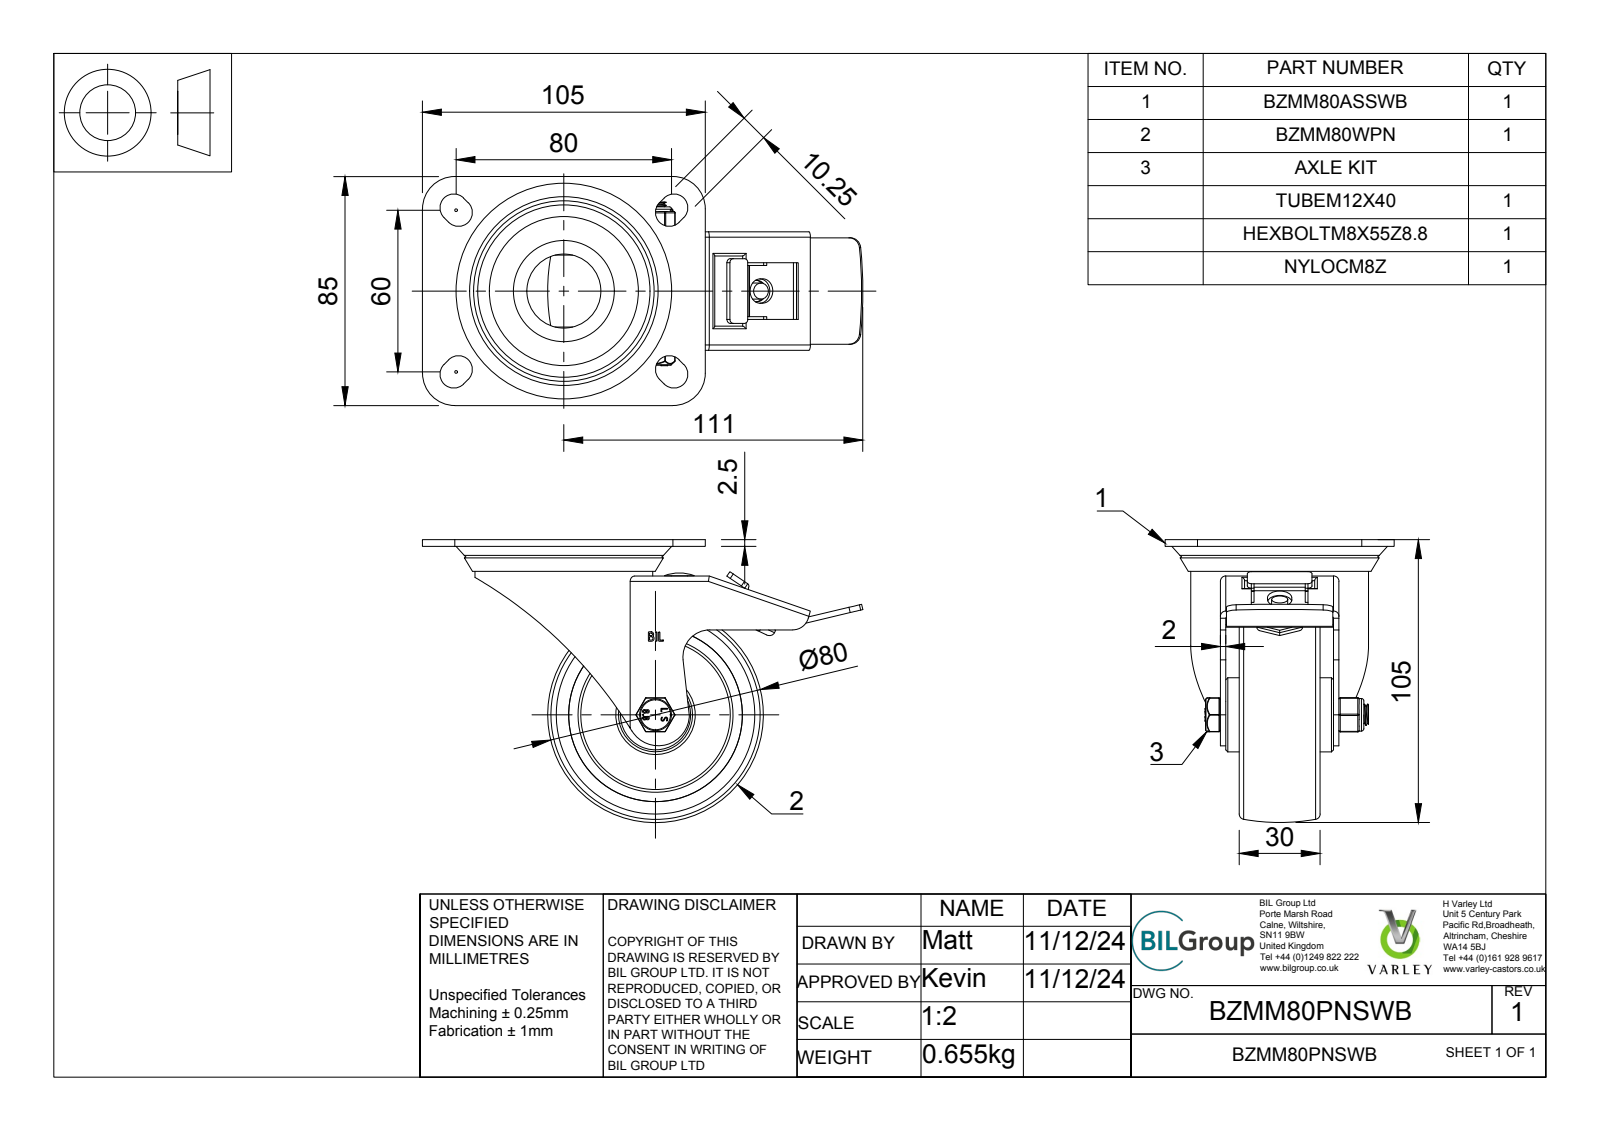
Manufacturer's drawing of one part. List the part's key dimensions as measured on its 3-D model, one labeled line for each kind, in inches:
Part name (STEP PRODUCT): BZMM80PNSWB v3; BZMM80ASSWB v1; ZINC PLATED, PRESSED STEEL TOP PLATE; ZINC PLATED, PRESSED STEEL TOP PLATE Geometry (+7 more)
STEP written by: Autodesk Translation Framework v13.20.0.188 (AP242_MANAGED_MODEL_BASED_3D_ENGINEERING_MIM_LF)
Units: inches
Bodies: 38 solids, 595 faces (293 planar, 184 cylindrical, 118 other)
Overall size (bounding box): 6.437 × 4.134 × 3.346
Volume: 9.975 in³ · Surface area: 166.1 in²
Round holes (diameter × count): ⌀0.026 ×2, ⌀0.315 ×2, ⌀0.236 ×1, ⌀0.323 ×1, ⌀0.331 ×1, ⌀0.339 ×1, ⌀0.488 ×1, ⌀1.083 ×1, ⌀2.205 ×1, ⌀2.264 ×1, ⌀2.441 ×1, ⌀2.539 ×1
Round bosses / shafts (diameter × count): ⌀2.598 ×1, ⌀1.24 ×1, ⌀1.083 ×1, ⌀0.476 ×1, ⌀0.469 ×1, ⌀0.453 ×1, ⌀0.31 ×1, ⌀0.254 ×1
Partial cylindrical surfaces — rounded edges, fillets, slot ends (radius × count): R0.02 ×24, R0.039 ×14, R0.01 ×12, R0.079 ×11, R0.202 ×8, R0.013 ×4, R0.025 ×4, R0.059 ×4
Main face-to-face distances: 0.079, 0.098, 0.197, 0.276, 1.654, 0.817, 0.915, 0.738, 0.837, 1.457
Hole centre spacings: 0.127, 0.098, 1.687
